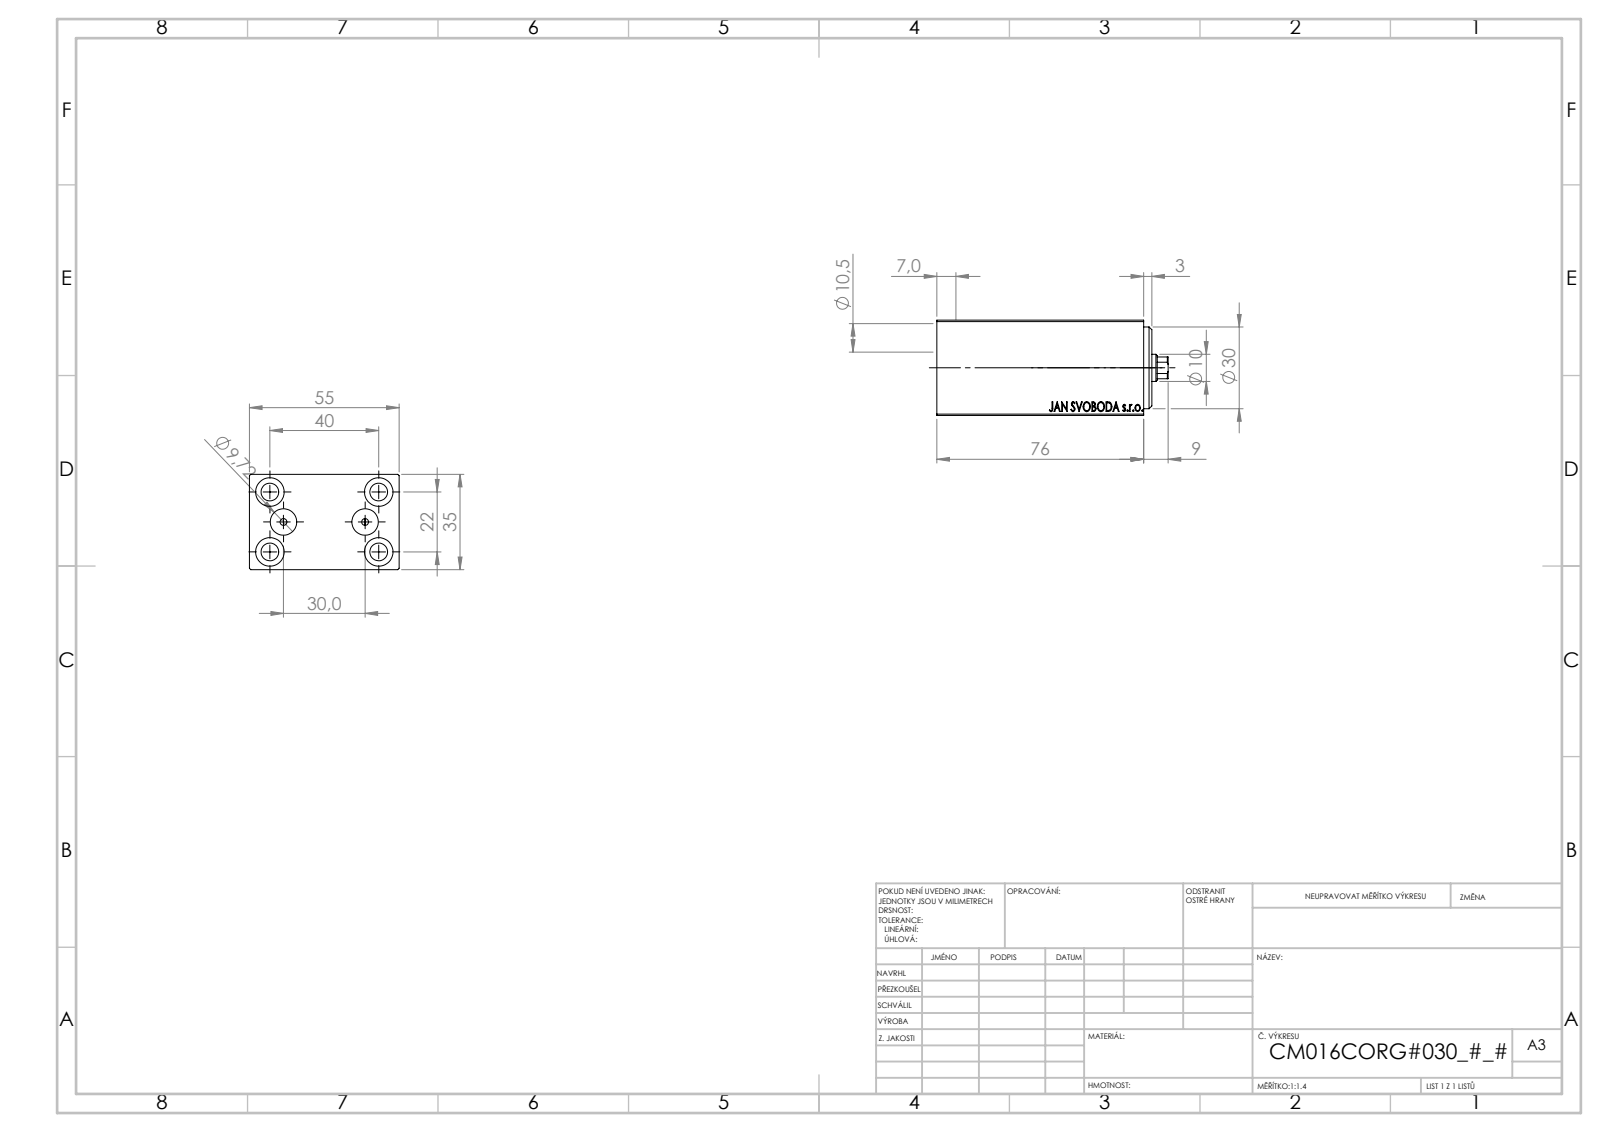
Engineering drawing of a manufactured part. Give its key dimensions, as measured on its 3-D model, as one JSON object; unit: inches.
{"part_name": "V450CM_C_Body; V450CM_C_VCP; V450CM_VC_B", "step_written_by": "SolidWorks 2019 (CONFIG_CONTROL_DESIGN)", "units": "inches", "bodies": {"solids": 3, "faces": 861, "planar": 409, "cylindrical": 58, "other": 394}, "overall_size": [3.346, 2.165, 1.378], "volume_in3": 7.904, "surface_area_in2": 56.93, "round_holes": [[0.256, 4], [0.413, 4], [0.098, 2], [0.383, 2], [0.177, 1], [0.394, 1], [0.531, 1], [0.571, 1], [0.63, 1], [0.709, 1], [1.181, 1]], "partial_cylinders_radius": [[0.177, 1]], "face_to_face_distances": [1.378, 2.165, 0.197, 2.795, 2.992, 0.118, 2.717, 2.598, 0.315, 3.11], "hole_center_spacings": [0.476, 0.899, 1.444, 0.591, 0.866, 1.575, 1.797, 1.181]}
